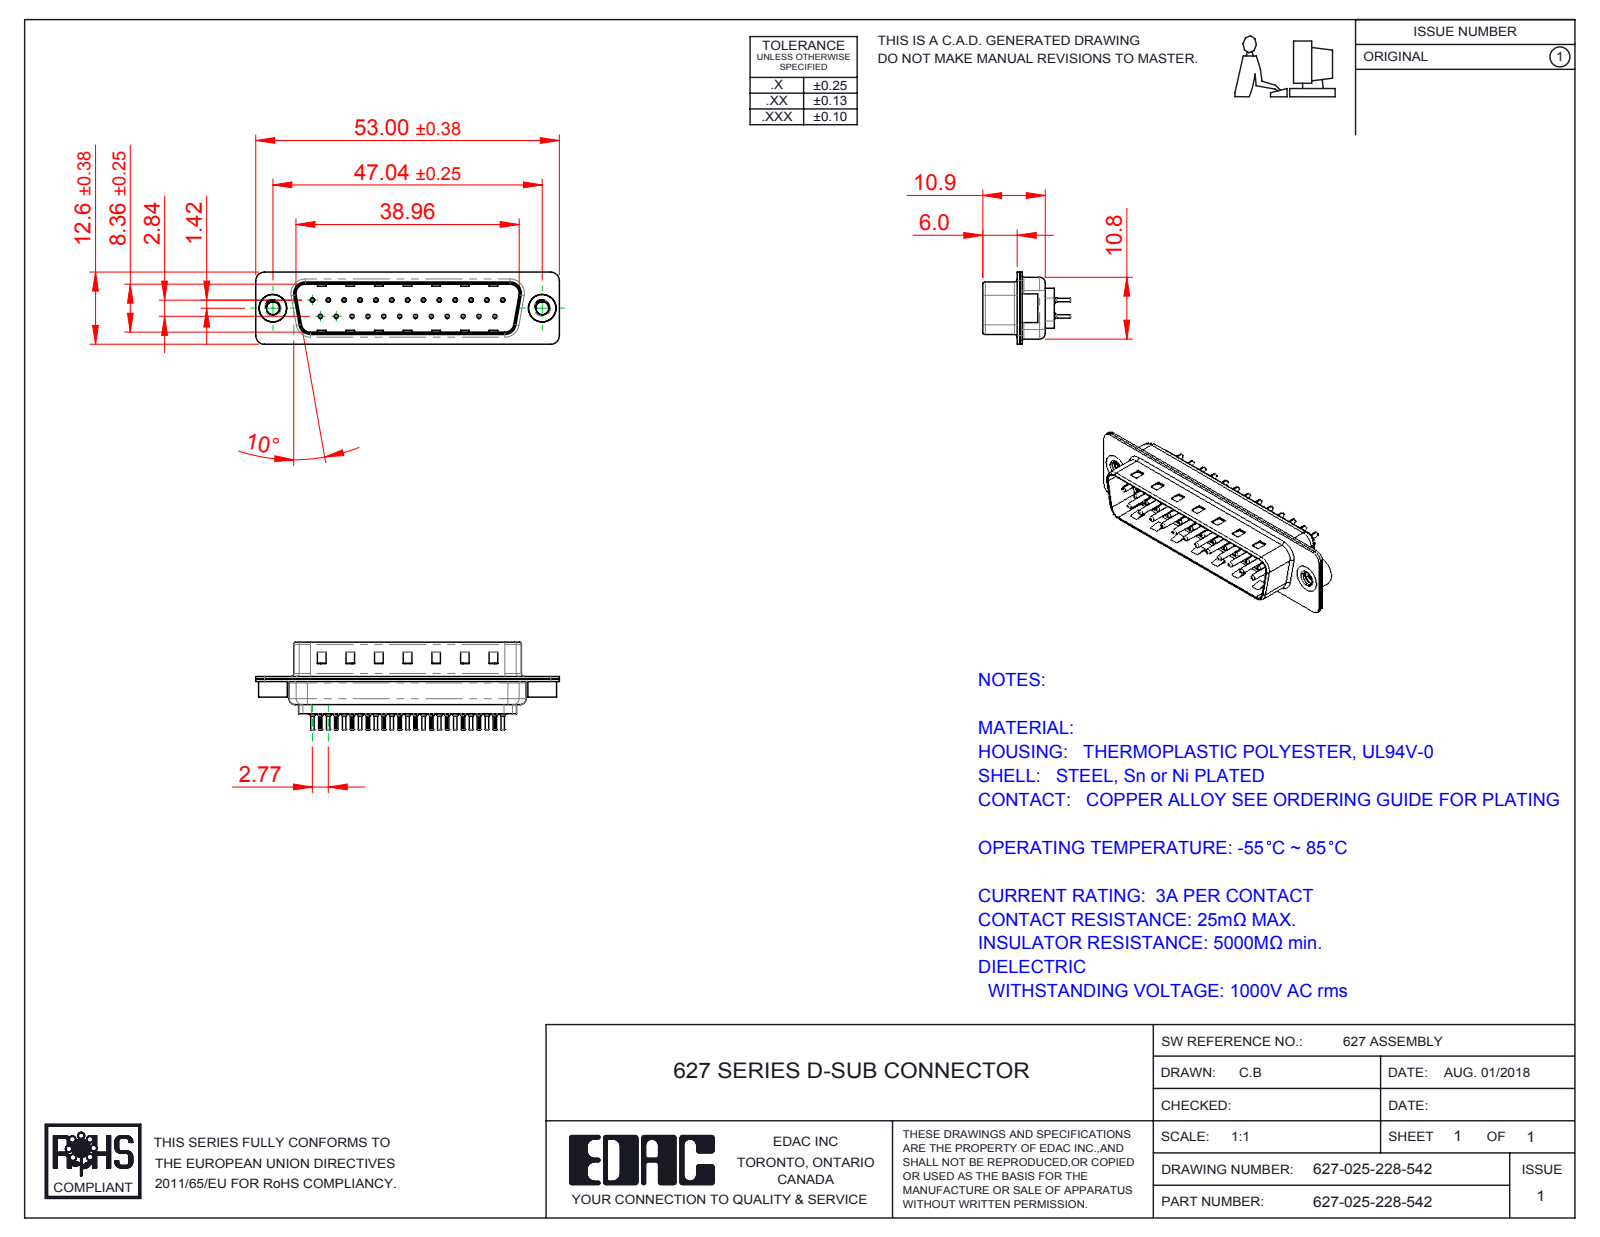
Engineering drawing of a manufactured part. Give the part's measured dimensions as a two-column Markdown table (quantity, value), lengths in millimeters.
| quantity | value |
| --- | --- |
| part name | 627 Shell Rear_25 Contacts; 627 Contact Row 1_28L; 627 Shell Front_25 Contacts; 627 4-40 Threaded Rivet (+3 more) |
| STEP written by | SolidWorks 2016 (CONFIG_CONTROL_DESIGN) |
| units | millimeters |
| bodies | 30 solids, 2826 faces (771 planar, 1062 cylindrical, 993 other) |
| overall size | 53 × 15.3 × 12.6 |
| volume | 2 672 mm³ |
| surface area | 7 667 mm² |
| round holes (diameter × count) | 0.2 × 25, 0.35 × 25, 1.1 × 25, 1.6 × 25, 2.26 × 2, 4 × 2, 4.8 × 2 |
| round bosses / shafts (diameter × count) | 2 × 25, 1.5 × 25, 0.75 × 25, 0.6 × 25, 5 × 2, 4.9 × 2 |
| partial cylindrical surfaces (radius × count) | 0.1 × 50, 1.5 × 16, 2 × 12, 0.5 × 8, 1.6 × 8, 0.25 × 4, 0.6 × 4, 0.65 × 4 |
| main face-to-face distances | 0.4, 0.45, 0.82, 9.58, 0.9, 8.76, 1.5, 1.4, 6.5, 6.05 |
| hole center spacings | 3.16, 8.31, 2.77, 5.54, 11.08, 16.62, 5.03, 5.04 |
